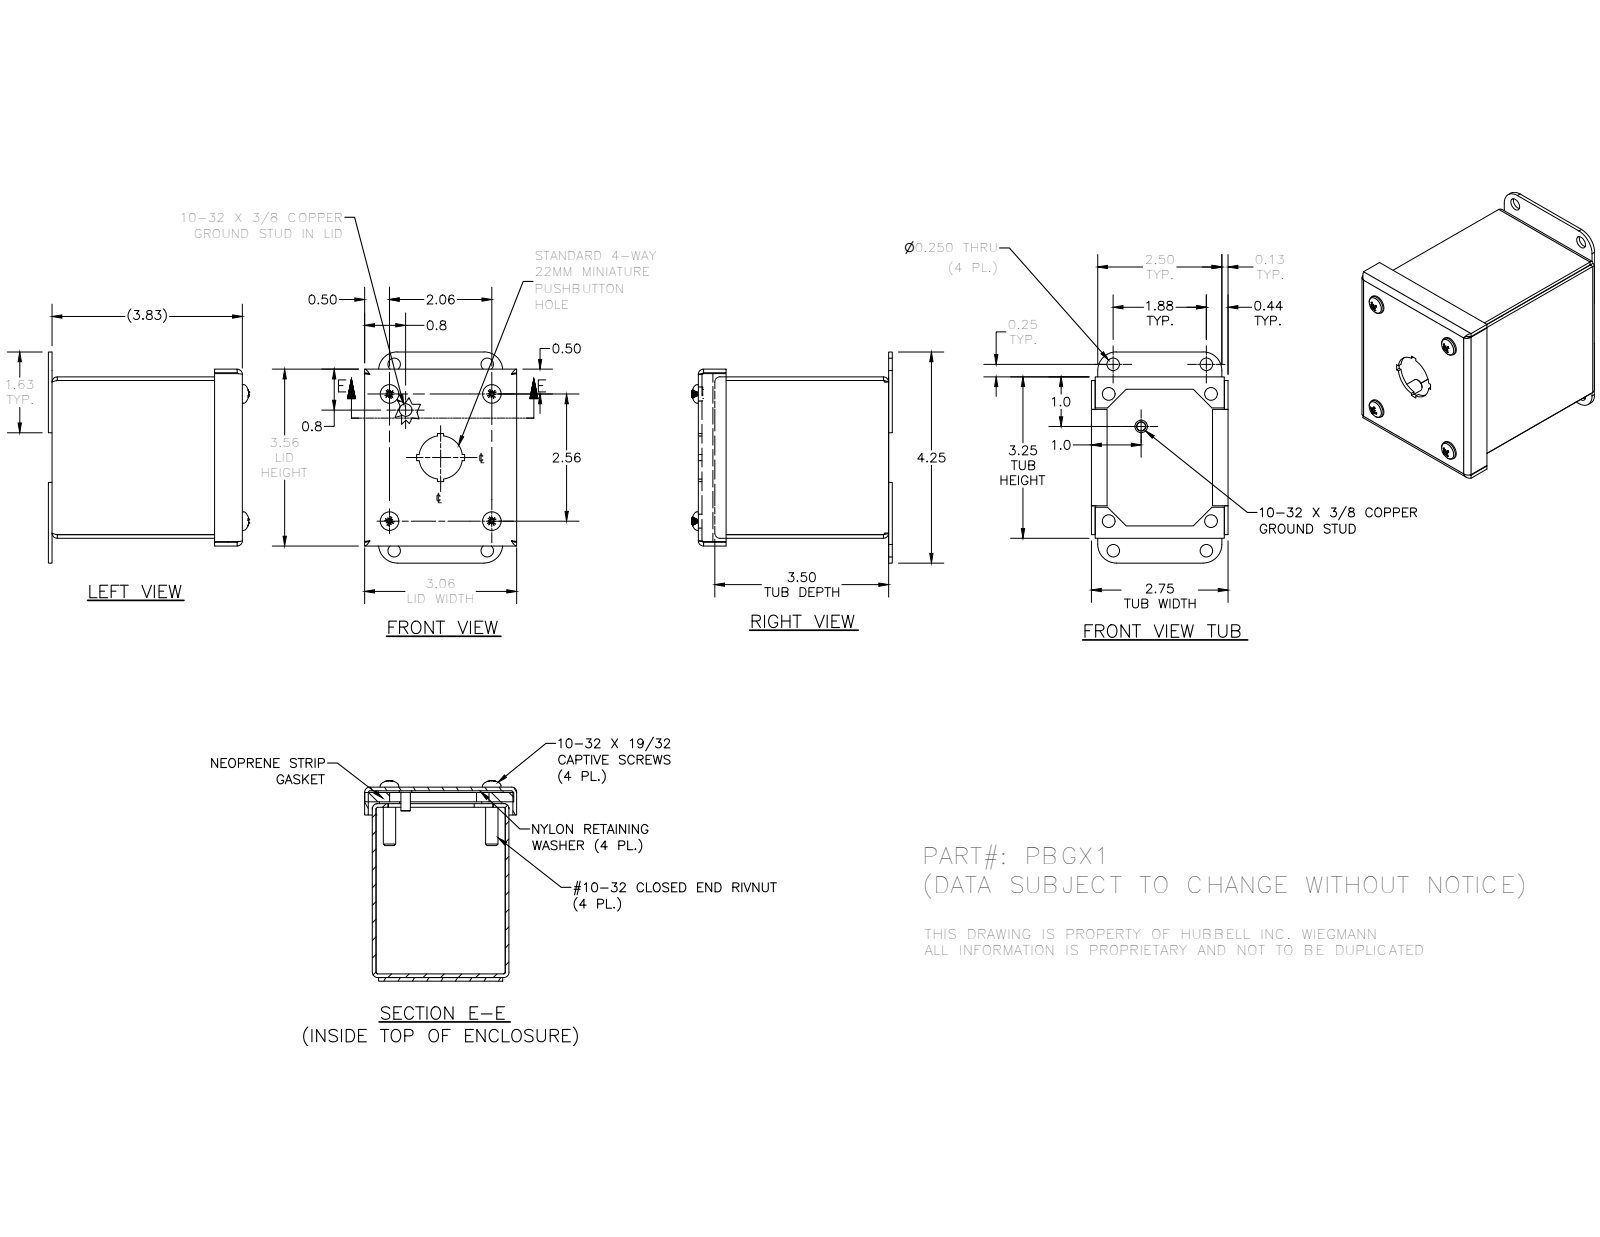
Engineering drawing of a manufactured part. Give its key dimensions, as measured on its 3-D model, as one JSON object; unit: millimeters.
{"part_name": "PBGX1BKP; 34984; 316270; 34817 (+5 more)", "step_written_by": "Autodesk Inventor 2016 (AUTOMOTIVE_DESIGN)", "units": "millimeters", "bodies": {"solids": 19, "faces": 494, "planar": 280, "cylindrical": 100, "other": 114}, "overall_size": [107.95, 102.51, 77.72], "volume_mm3": 109265, "surface_area_mm2": 114880, "round_holes": [[3.96, 4], [4.98, 4], [6.35, 4], [6.53, 4], [7.06, 4], [7.14, 4], [7.95, 4], [22.22, 1]], "round_bosses_or_shafts": [[4.83, 6], [11.51, 4], [10.31, 4], [9.47, 4], [6.3, 4], [6.35, 2]], "partial_cylinders_radius": [[0.79, 12], [2.67, 12], [2.27, 4], [9.53, 4]], "face_to_face_distances": [1.88, 67.97, 80.67, 95.45, 97.33, 3.94, 69.85, 66.09, 82.55, 78.79], "hole_center_spacings": [15.29, 80.17, 94.45, 53.25, 41.73, 41.74, 47.64, 52.21]}
